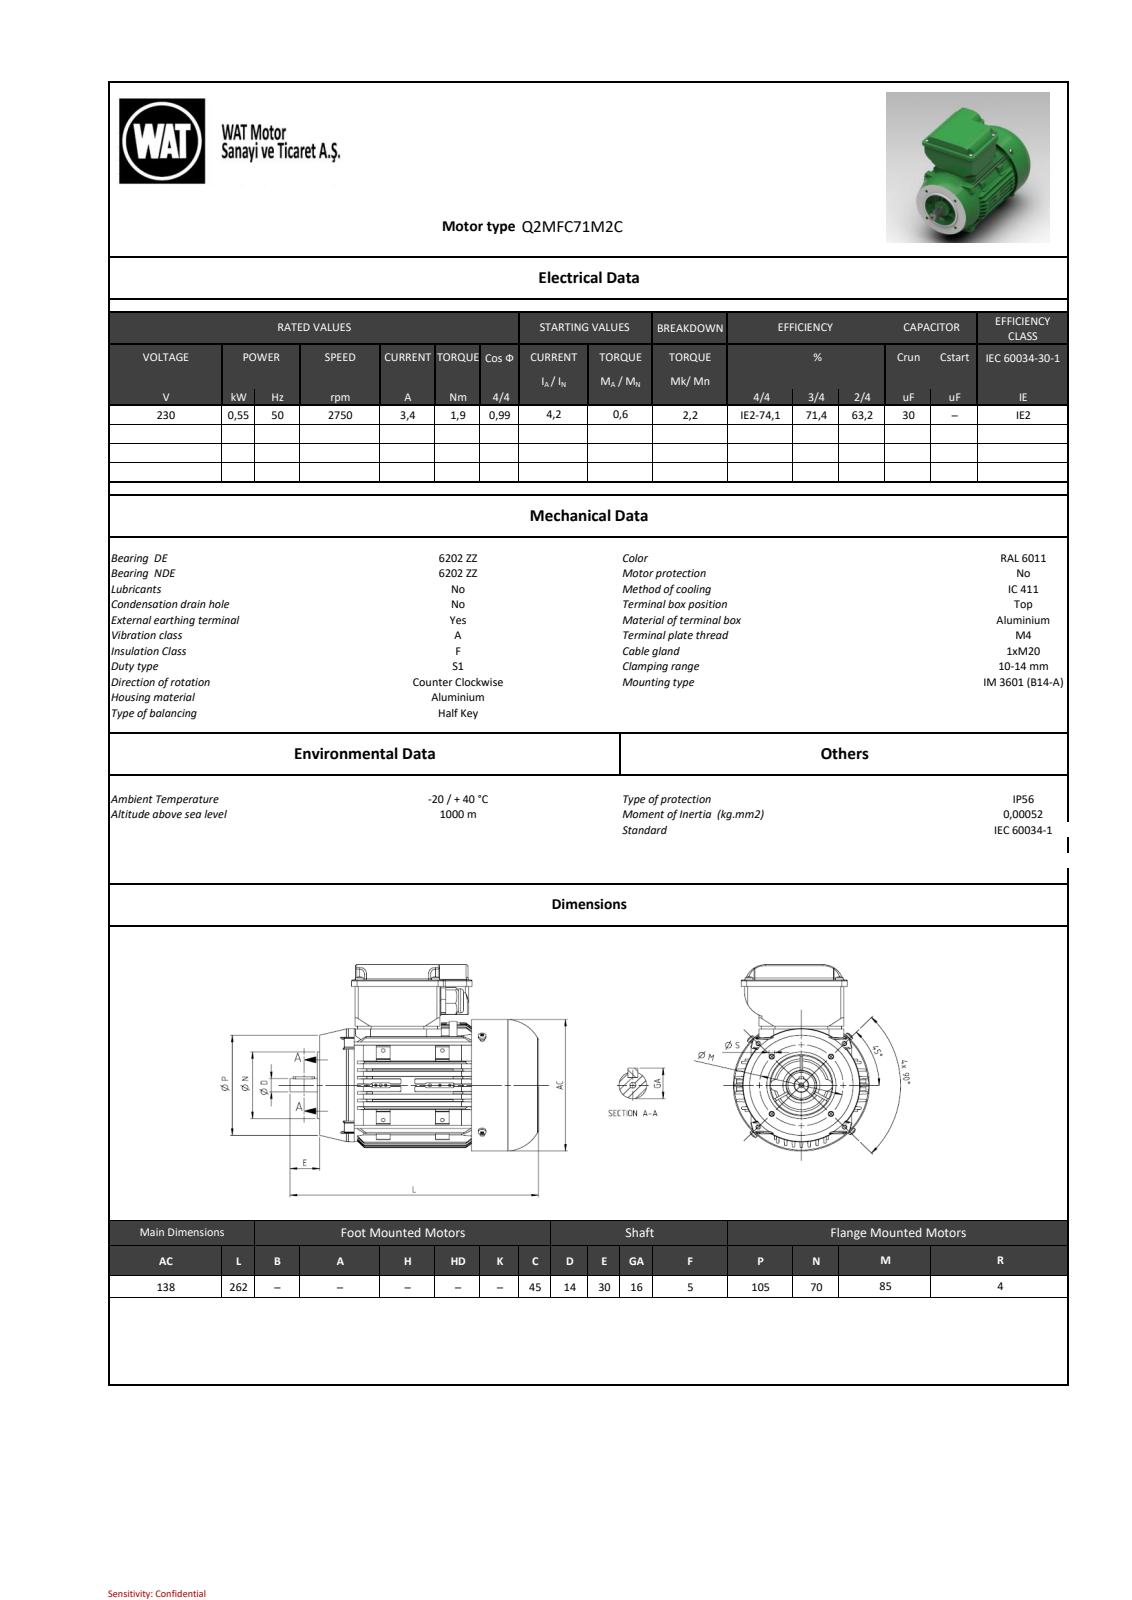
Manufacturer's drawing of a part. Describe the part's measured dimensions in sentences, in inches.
The part is named "BY6434017xx_004-TK_QM63-80; BY6424130xx_004-TKK_QM63-80; BY6432003xx_006-MOTOR_KAPAGI_QS71_FC_ISLEME; 641304741_AZ-KAMA PARALEL A 5x5x22 St50 DIN6885 (+6 more)". Its 3-D file was written by "SIEMENS PLM Software NX2206.8101 (AUTOMOTIVE_DESIGN)". It is 24 solids with 2647 faces: 1275 planar, 733 cylindrical and 639 other. Overall it measures 10.315 by 7.697 by 5.433 inches. Its volume is 44.16 cubic inches and its surface area 739.4 square inches. Round holes: 8 of diameter 0.144, 8 of diameter 0.177, 7 of diameter 0.118, 6 of diameter 0.098, 5 of diameter 0.13, 4 of diameter 0.157, 4 of diameter 0.183, 4 of diameter 0.189, 3 of diameter 0.146, 2 of diameter 0.181, 1 of diameter 0.197, 1 of diameter 0.236. Round bosses or shafts: 8 of diameter 0.315, 8 of diameter 0.157, 8 of diameter 0.118, 4 of diameter 0.472, 4 of diameter 0.13, 1 of diameter 5.433, 1 of diameter 2.756, 1 of diameter 1.024. Partial cylindrical surfaces (rounded edges, fillets, slot ends): 135 of radius 0.039, 51 of radius 0.079, 36 of radius 0.047, 35 of radius 0.02, 20 of radius 0.197, 16 of radius 0.128, 16 of radius 0.394, 14 of radius 0.098. The main face-to-face distances are 0.118, 7.657, 1.417, 0.157, 6.24, 1.26, 7.539, 0.039, 2.539, 0.079. The hole center spacings are 3.442, 2.165, 1.441, 2.362, 1.467, 2.432, 2.436, 2.634.
